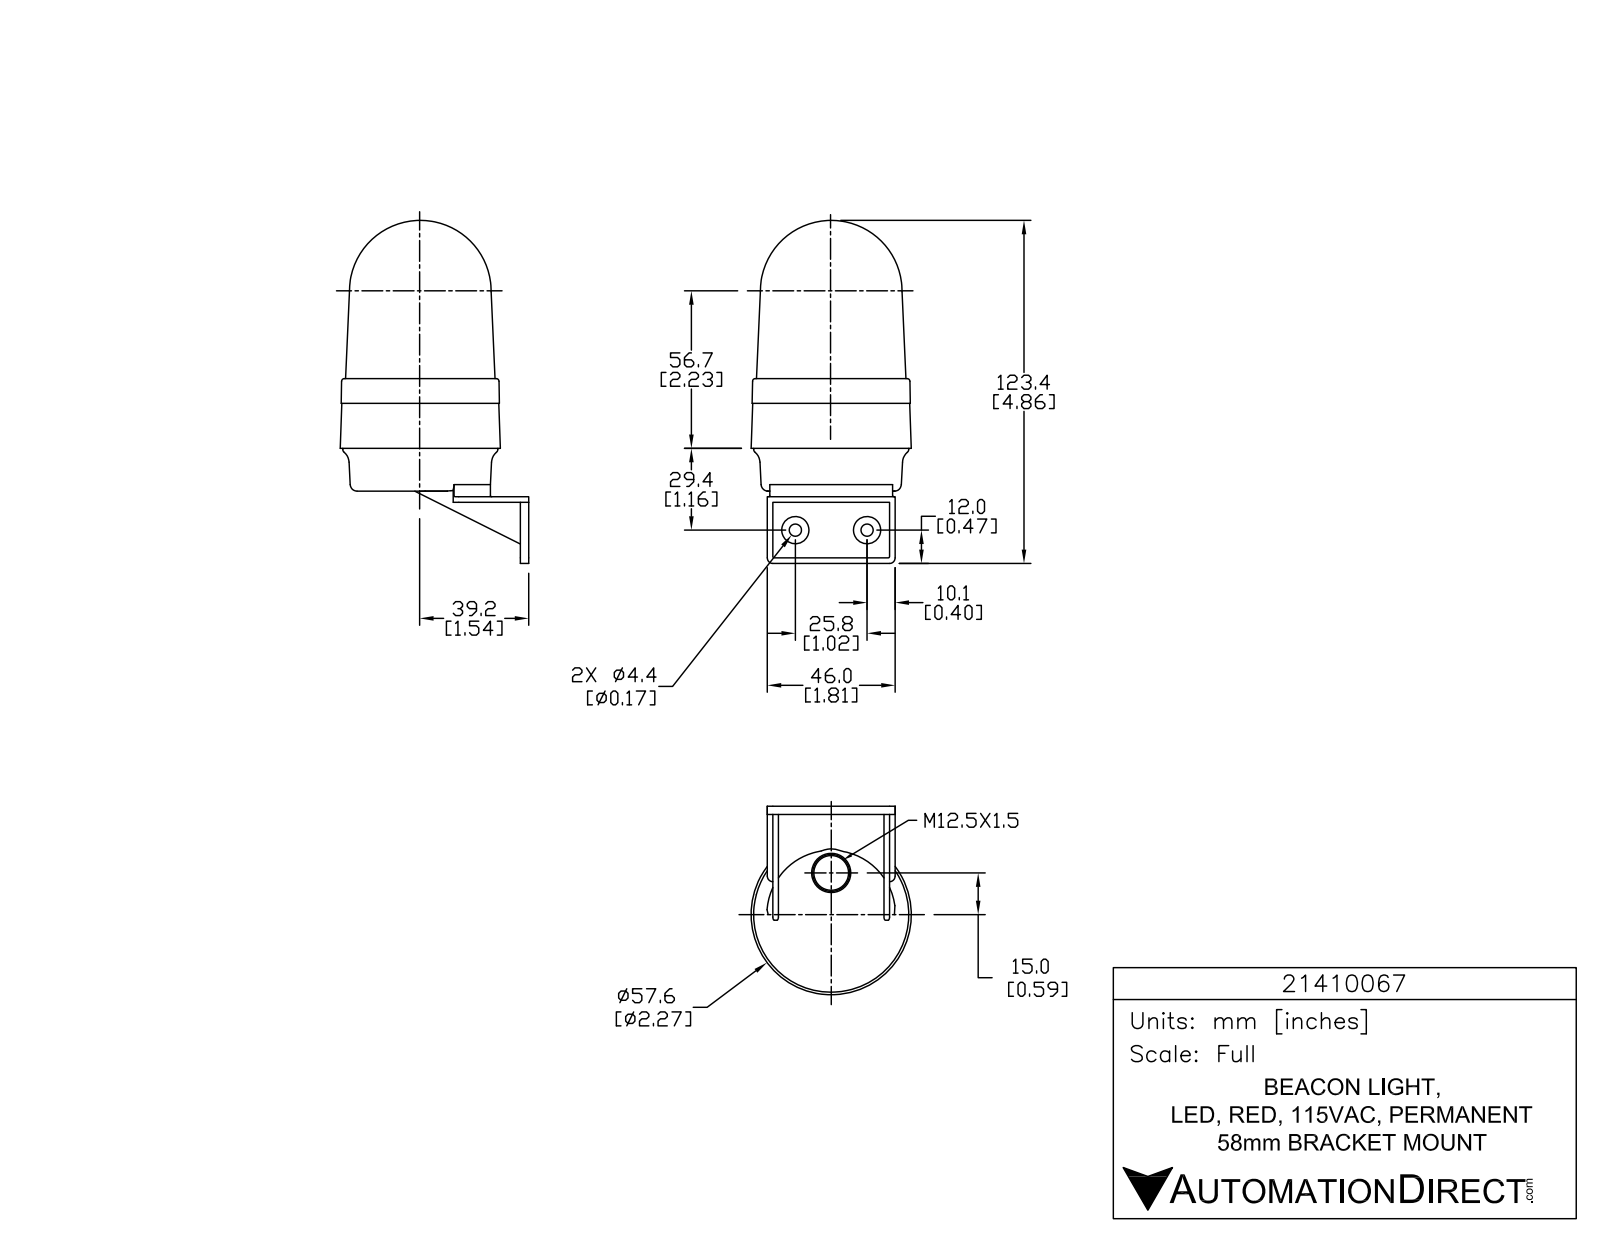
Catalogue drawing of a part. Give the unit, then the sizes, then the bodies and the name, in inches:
Units: inches
Overall size (bounding box): 4.858 × 2.852 × 2.407
Round holes (diameter × count): ⌀0.039 ×3, ⌀0.173 ×2
Round bosses / shafts (diameter × count): ⌀0.226 ×3, ⌀0.056 ×3, ⌀0.386 ×2, ⌀2.197 ×1
Partial cylindrical surfaces — rounded edges, fillets, slot ends (radius × count): R0.008 ×6, R0.008 ×6, R0.008 ×6, R0.02 ×6, R0.131 ×6, R0.079 ×4, R0.004 ×3, R0.005 ×3
Main face-to-face distances: 0.079, 0.157, 1.575, 1.654, 0.039, 0.118, 1.496, 0.866, 0.945, 0.764
Hole centre spacings: 1.016
Volume: 12.43 in³ · Surface area: 37.49 in²
Bodies: 1 solid, 828 faces (551 planar, 179 cylindrical, 98 other)
Part name (STEP PRODUCT): 21410067
STEP written by: SolidWorks 2015 (AUTOMOTIVE_DESIGN)
